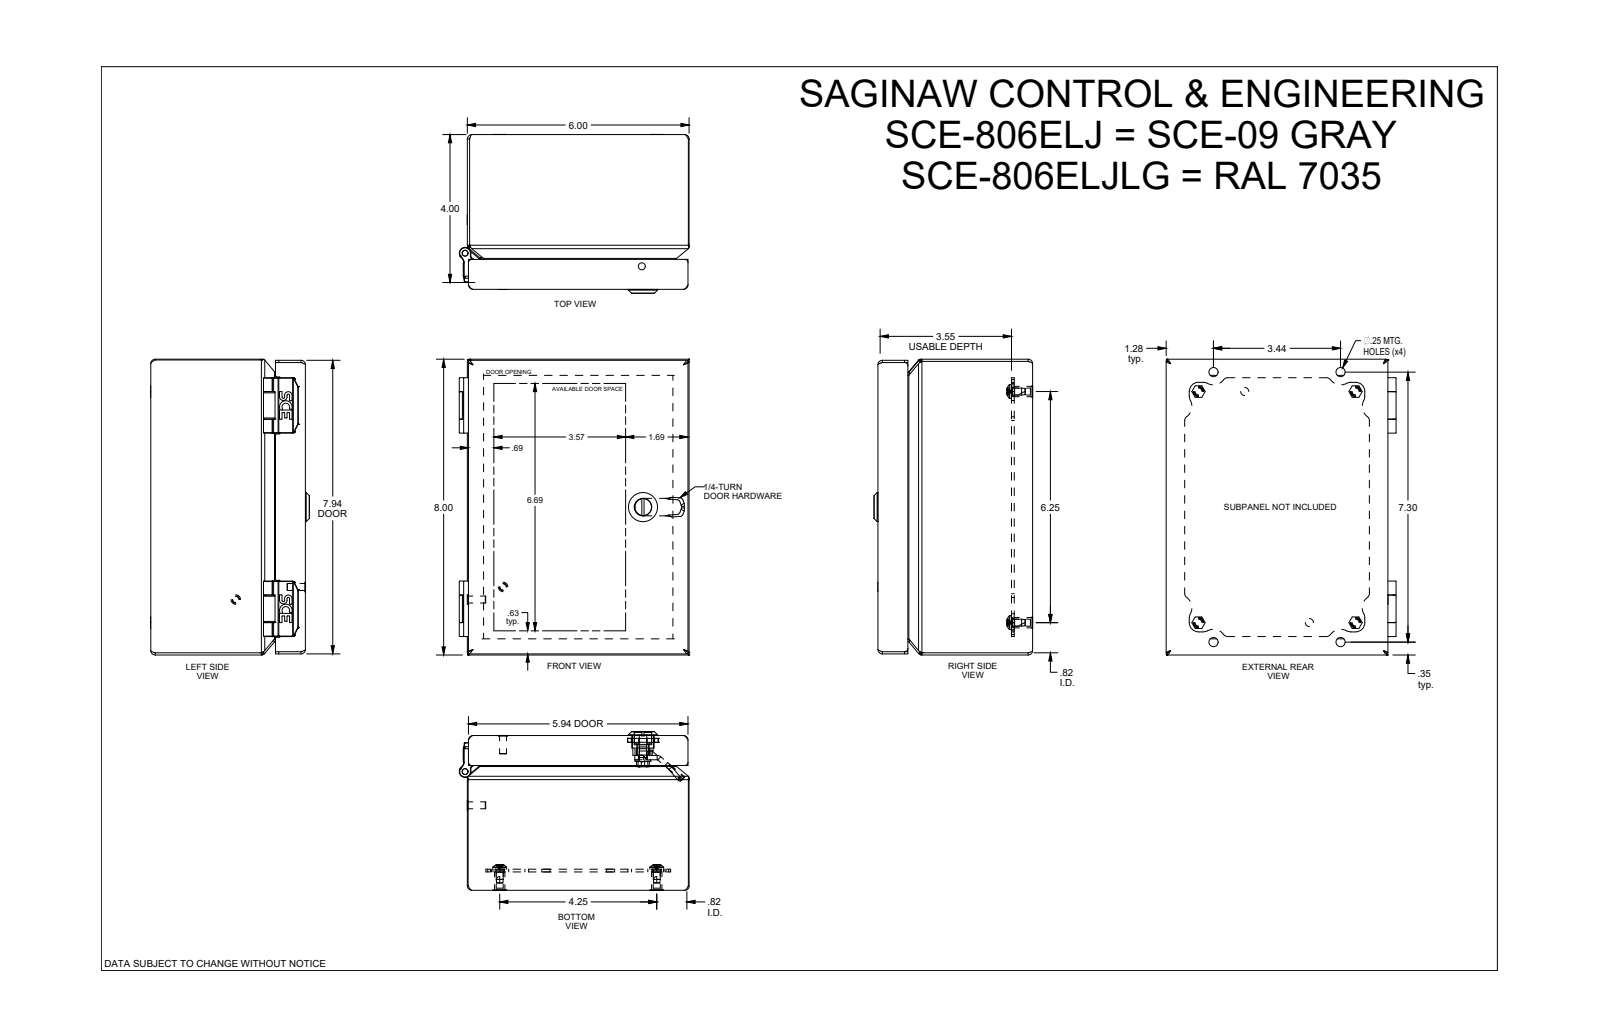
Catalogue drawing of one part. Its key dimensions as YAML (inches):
part_name: "SCE-806ELJ"
step_written_by: "SolidWorks 2021 (AUTOMOTIVE_DESIGN)"
units: inches
bodies: {solids: 22, faces: 1290, planar: 401, cylindrical: 386, other: 503}
overall_size: [8, 6.22, 4.292]
volume: 16.84
surface_area: 543.1
round_holes:
  - {diameter: 0.25, count: 4}
  - {diameter: 0.284, count: 4}
  - {diameter: 0.17, count: 2}
  - {diameter: 0.218, count: 2}
  - {diameter: 0.158, count: 1}
  - {diameter: 0.2, count: 1}
  - {diameter: 0.239, count: 1}
  - {diameter: 0.254, count: 1}
  - {diameter: 0.269, count: 1}
  - {diameter: 0.282, count: 1}
  - {diameter: 0.326, count: 1}
  - {diameter: 0.475, count: 1}
round_bosses_or_shafts:
  - {diameter: 0.188, count: 5}
  - {diameter: 0.373, count: 4}
  - {diameter: 0.284, count: 4}
  - {diameter: 0.479, count: 2}
  - {diameter: 0.26, count: 2}
  - {diameter: 0.1, count: 2}
  - {diameter: 0.02, count: 2}
  - {diameter: 0.788, count: 1}
partial_cylinders:
  - {radius: 0.106, count: 66}
  - {radius: 0.005, count: 36}
  - {radius: 0.008, count: 32}
  - {radius: 0.013, count: 21}
  - {radius: 0.05, count: 16}
  - {radius: 0.025, count: 12}
  - {radius: 0.25, count: 12}
  - {radius: 0.01, count: 10}
face_to_face_distances: [0.059, 0.062, 5.941, 4.123, 4.185, 4.126, 4.064, 7.941, 0.571, 0.512]
hole_center_spacings: [4.25, 6.25, 6.251, 7.558, 6.933, 1.25, 1.25, 3]
